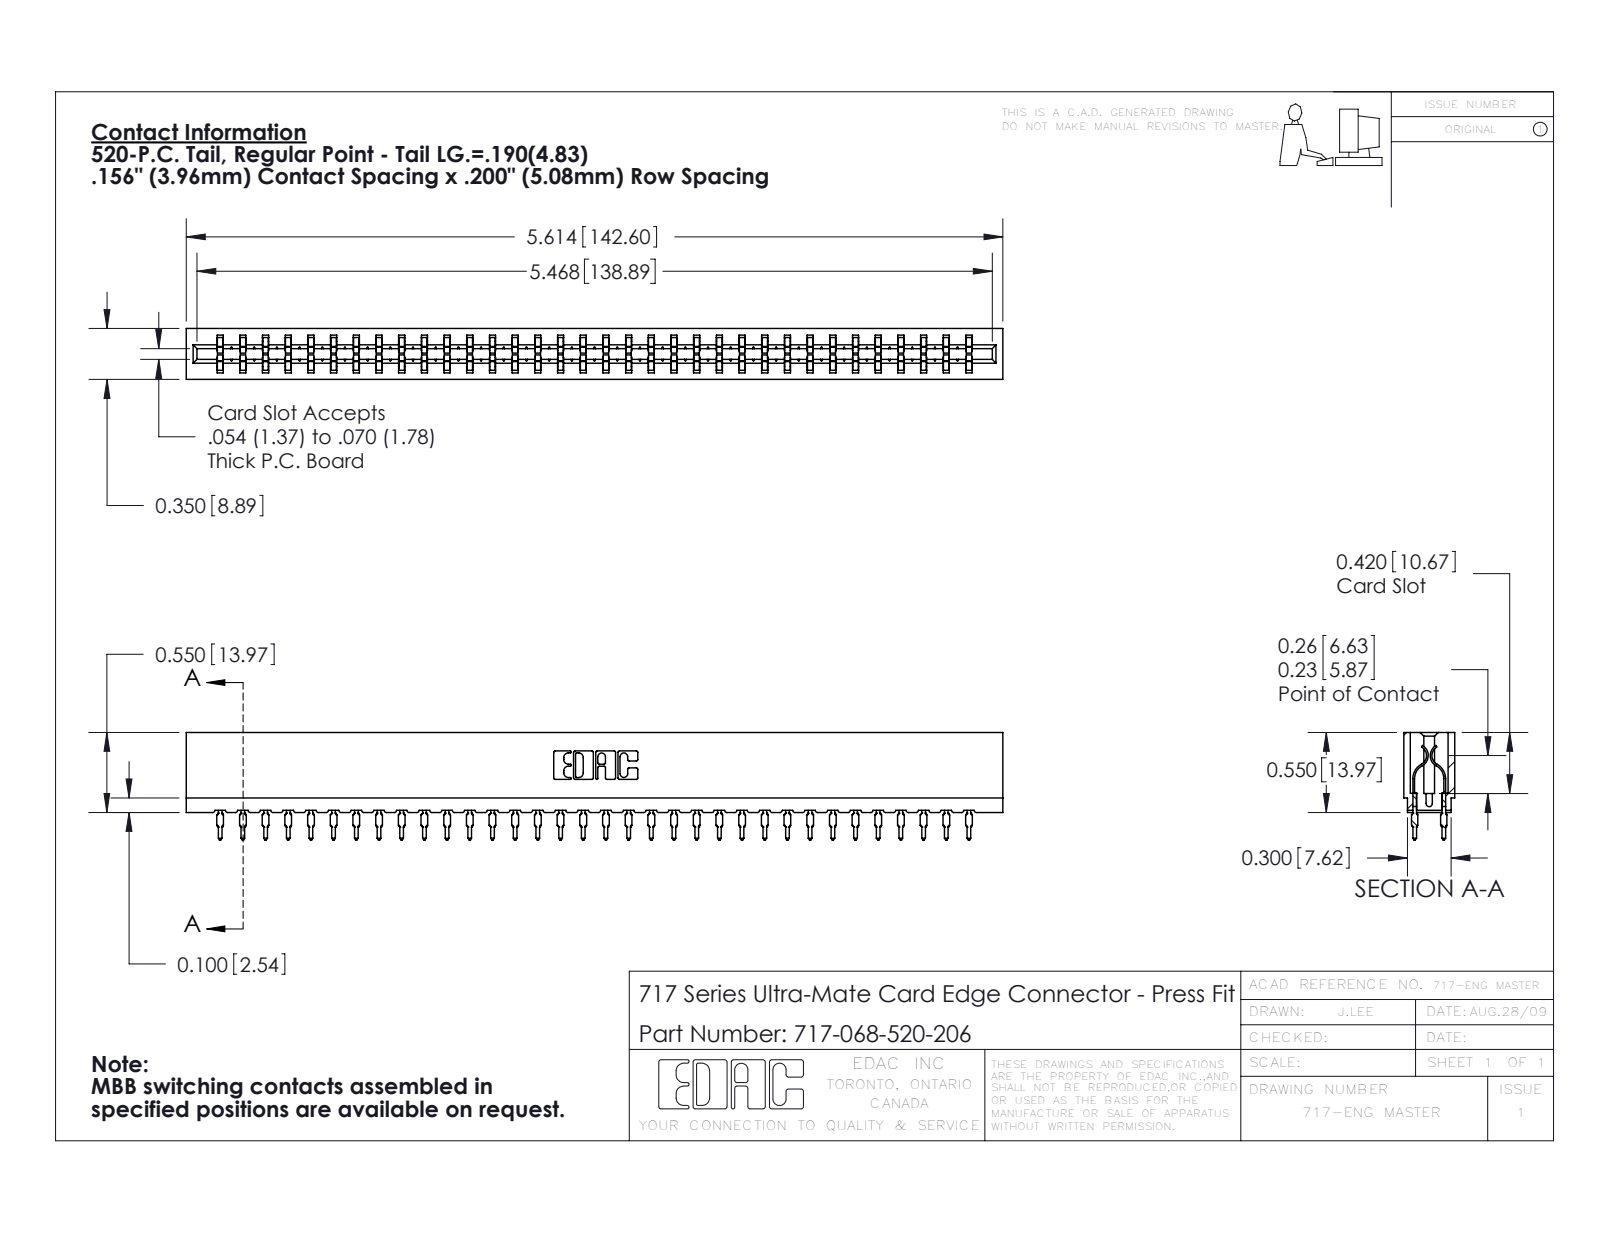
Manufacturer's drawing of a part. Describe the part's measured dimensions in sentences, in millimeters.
The part is named "745-292-001_520; 717-068-520-206; 717 Part_Insulator Option - 06". Its 3-D file was written by "SolidWorks 2016 (CONFIG_CONTROL_DESIGN)". It is 69 solids with 6214 faces: 3216 planar, 1230 cylindrical and 1768 other. Overall it measures 142.6 by 18.8 by 8.9 millimeters. Its volume is 12 300 cubic millimeters and its surface area 18 410 square millimeters. Partial cylindrical surfaces (rounded edges, fillets, slot ends): 136 of radius 0.5, 68 of radius 0.4, 22 of radius 0.3, 8 of radius 0.1, 8 of radius 0.3, 6 of radius 0.2, 6 of radius 0.8, 3 of radius 0.7. The main face-to-face distances are 5.4, 3.5, 8.9, 1.6, 7.3, 1.9, 3.8, 1.9, 4, 1.1.
